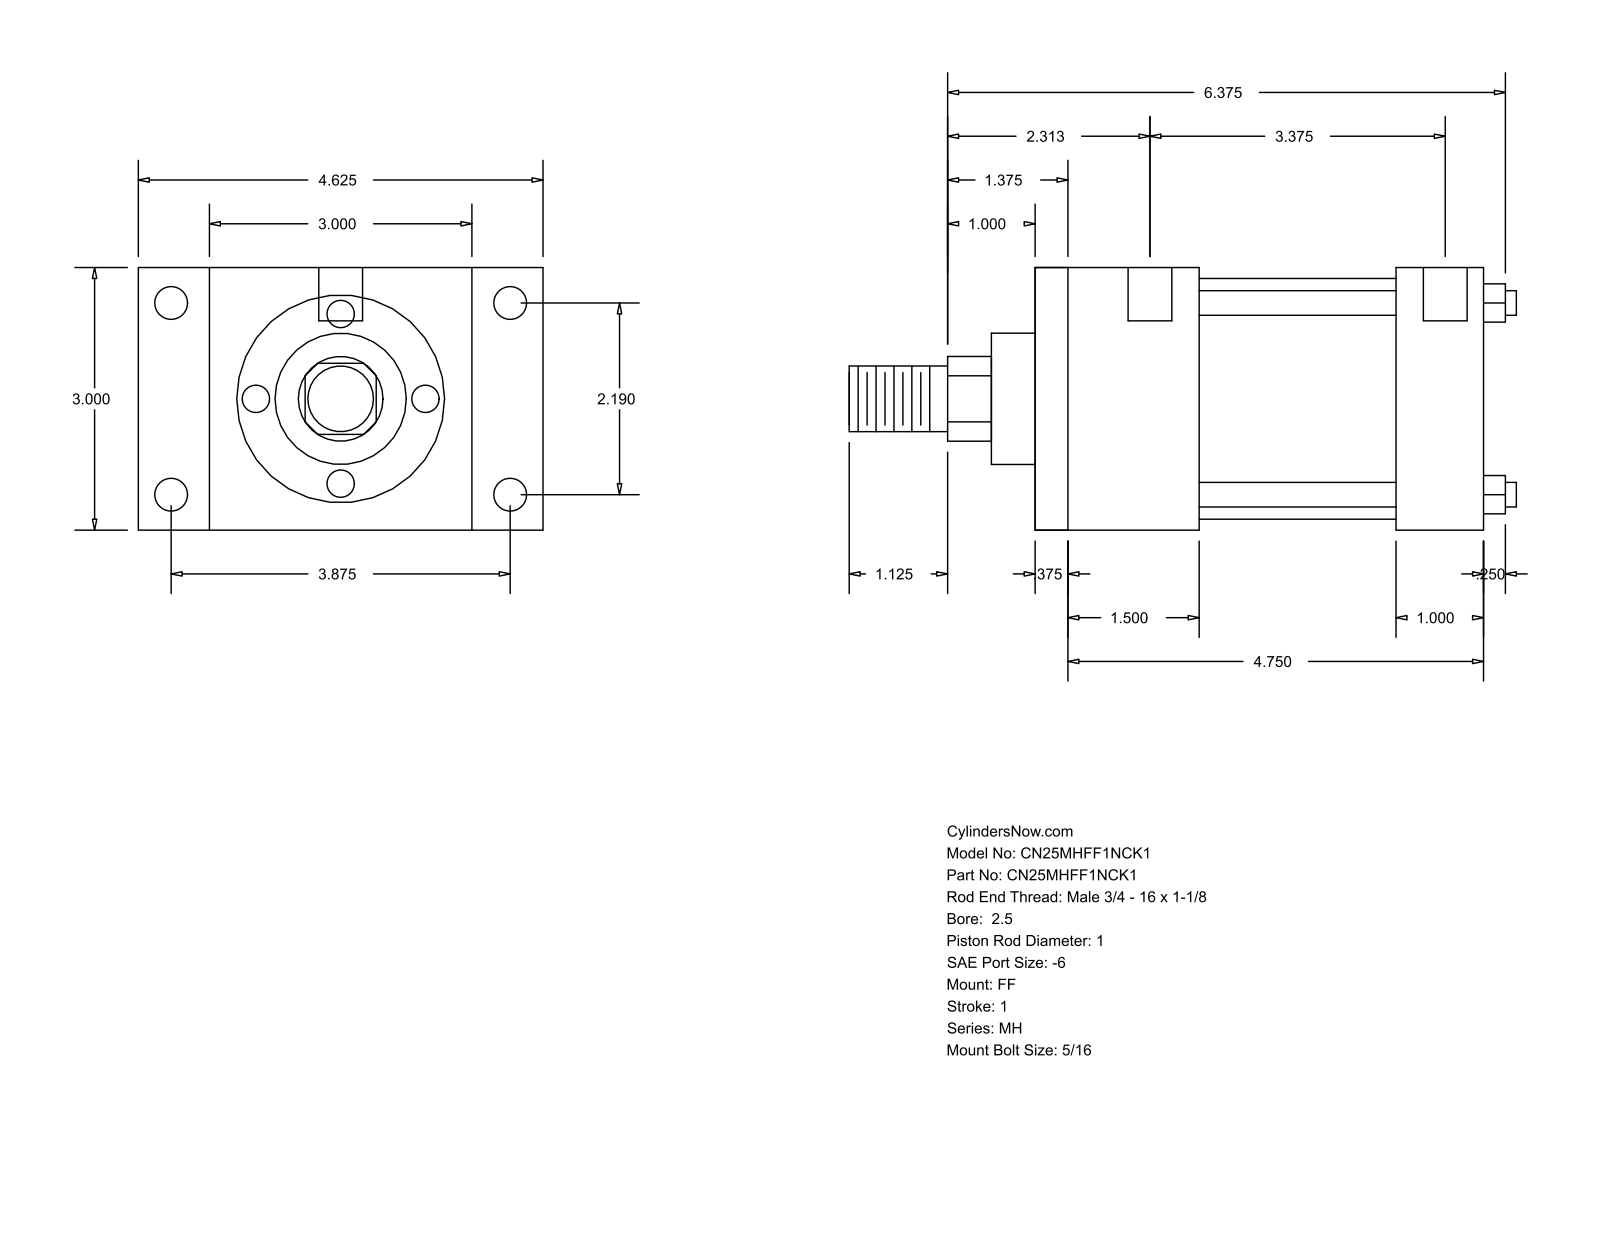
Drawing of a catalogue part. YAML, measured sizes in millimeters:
part_name: "MH_FF__0250_1"
step_written_by: "GSSL Pune (CONFIG_CONTROL_DESIGN)"
units: millimeters
bodies: {solids: 0, faces: 92, planar: 64, cylindrical: 28, other: 0}
overall_size: [193.68, 117.47, 76.2]
round_holes:
  - {diameter: 5.56, count: 4}
  - {diameter: 9.53, count: 4}
  - {diameter: 12.7, count: 2}
round_bosses_or_shafts:
  - {diameter: 7.14, count: 4}
  - {diameter: 69.85, count: 1}
  - {diameter: 38.1, count: 1}
  - {diameter: 25.4, count: 1}
  - {diameter: 19.05, count: 1}
partial_cylinders:
  - {radius: 12.29, count: 1}
face_to_face_distances: [76.2, 130.17, 120.65, 9.52, 25.39, 47.63, 104.78, 38.11, 95.26, 57.15]
hole_center_spacings: [55.62, 93.66, 98.42, 113.05, 3.18, 4.76, 85.72, 88.9]
